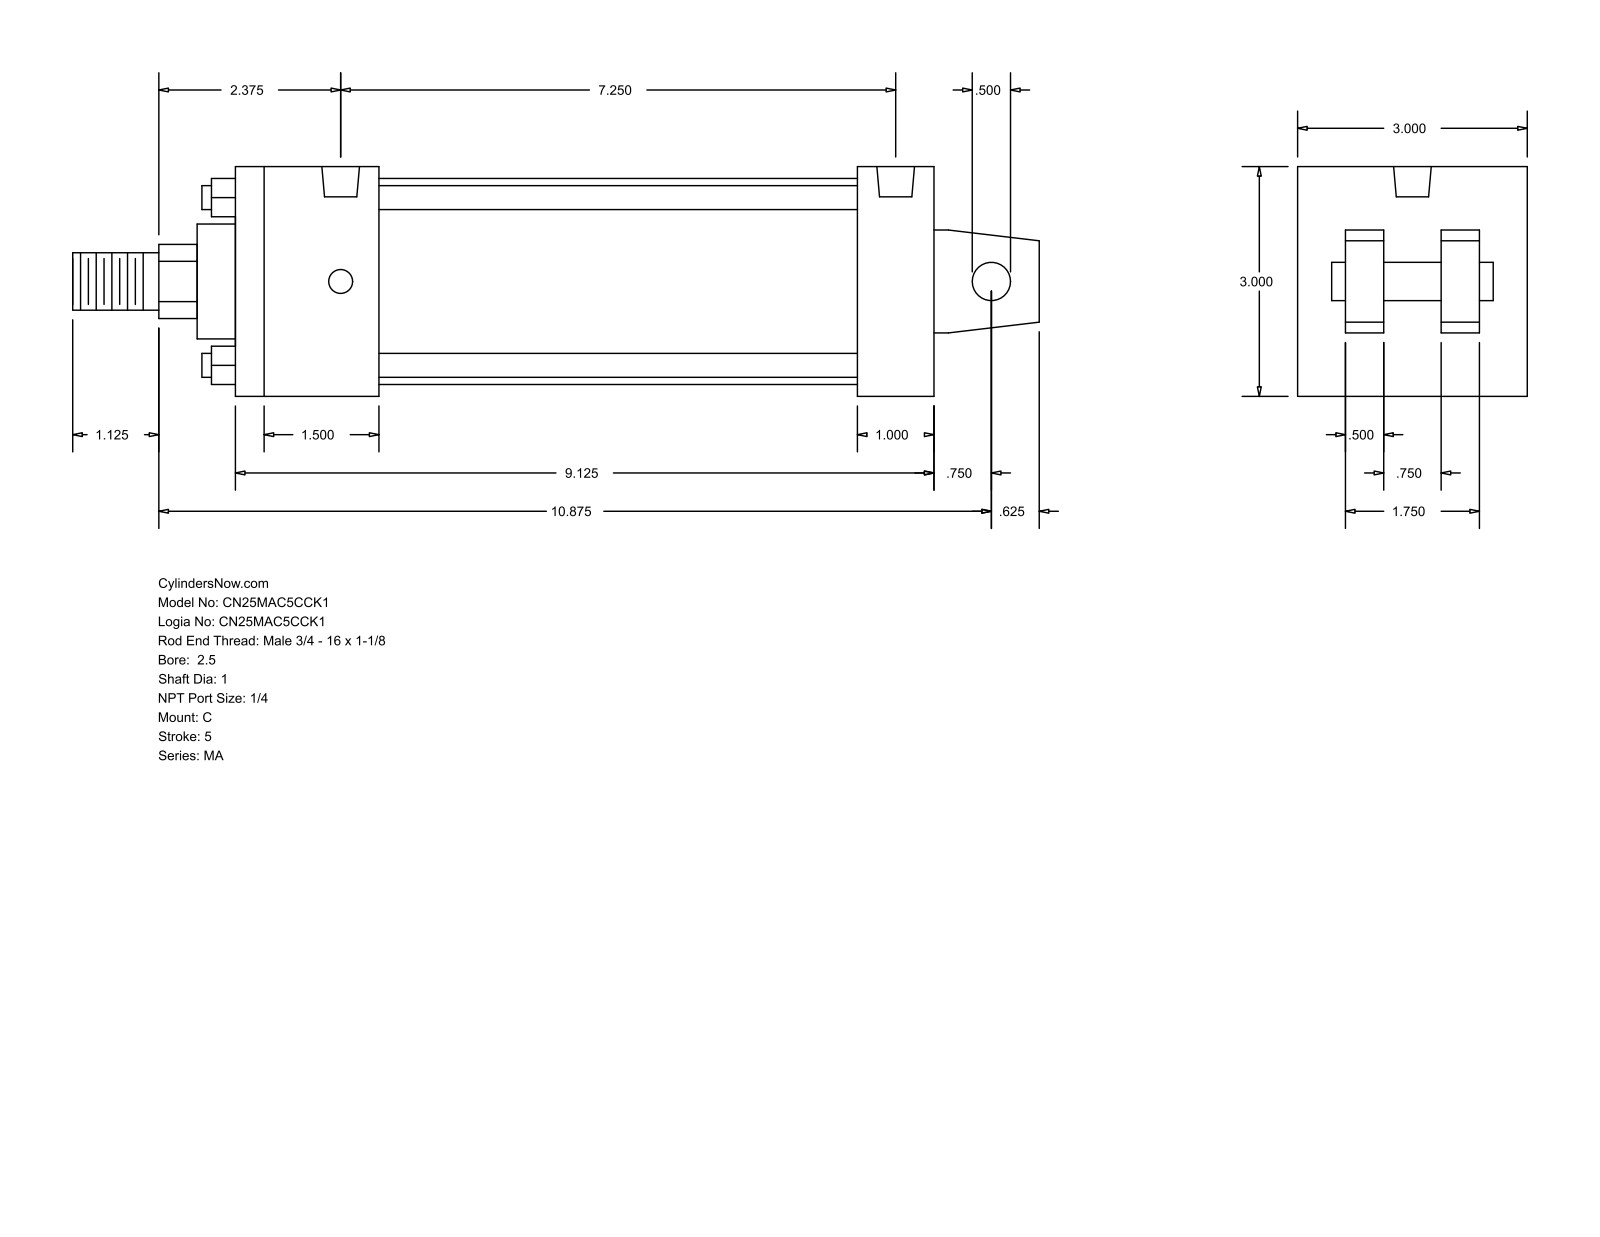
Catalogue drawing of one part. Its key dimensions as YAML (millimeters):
part_name: "MA_C__0250_1"
step_written_by: "GSSL Pune (CONFIG_CONTROL_DESIGN)"
units: millimeters
bodies: {solids: 0, faces: 103, planar: 76, cylindrical: 27, other: 0}
overall_size: [320.68, 76.2, 76.2]
round_holes:
  - {diameter: 7.94, count: 4}
  - {diameter: 12.49, count: 2}
round_bosses_or_shafts:
  - {diameter: 7.94, count: 4}
  - {diameter: 68.33, count: 1}
  - {diameter: 38.1, count: 1}
  - {diameter: 25.4, count: 1}
  - {diameter: 19.05, count: 1}
  - {diameter: 12.7, count: 1}
partial_cylinders:
  - {radius: 12.29, count: 1}
face_to_face_distances: [76.2, 231.78, 47.63, 12.7, 60.33, 15.87, 25.4, 28.57, 206.38, 158.75]
hole_center_spacings: [184.14]
